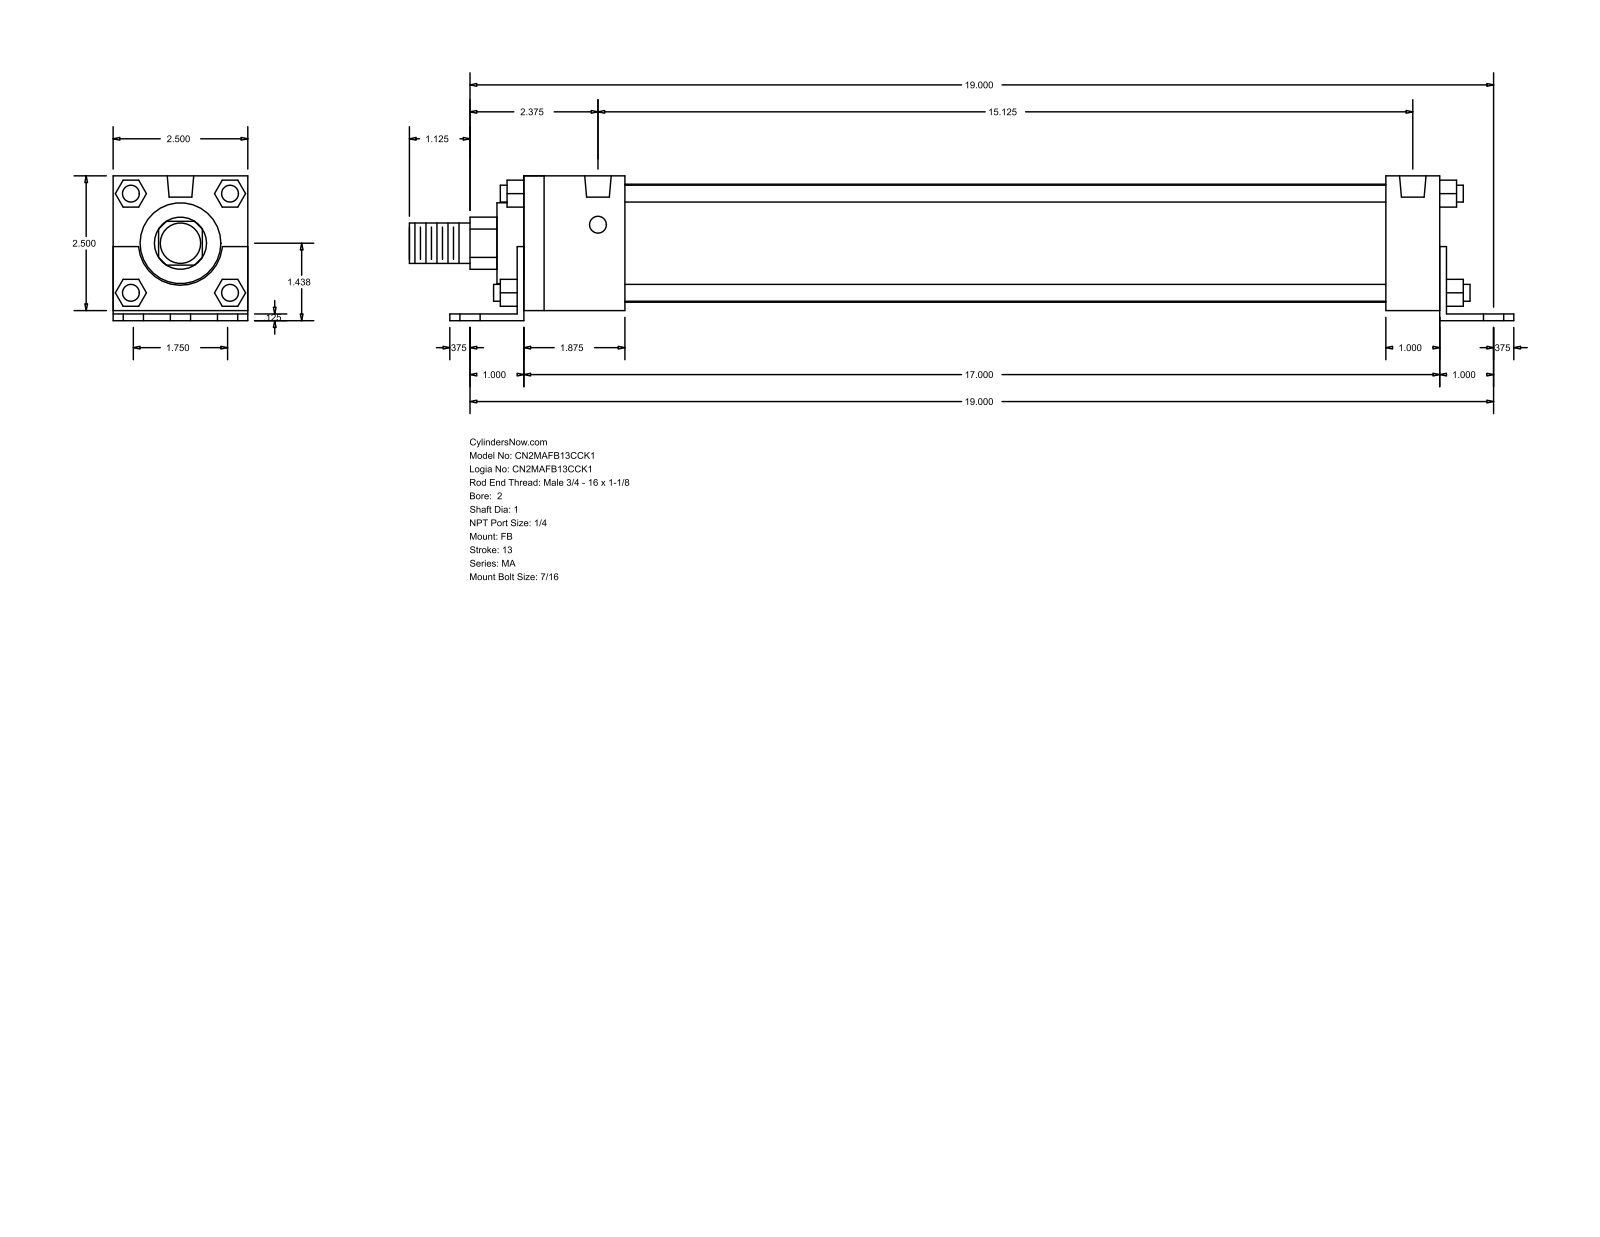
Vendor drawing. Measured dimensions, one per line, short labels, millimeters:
name: MA_FB__0200_1
written by: GSSL Pune (CONFIG_CONTROL_DESIGN)
unit: mm
bodies: 0 solids, 140 faces (105 planar, 35 cylindrical, 0 other)
size: 520.7 × 68.26 × 63.5
holes: 6× ⌀11.11, 4× ⌀7.94, 2× ⌀12.49
bosses: 4× ⌀7.94, 1× ⌀55.63, 1× ⌀38.1, 1× ⌀25.4, 1× ⌀19.05
rounds: 1× R12.29, 1× R19.81
face distances: 63.5, 3.17, 4.76, 68.26, 1.59, 65.09, 12.7, 3.18, 431.8, 434.98
hole spacings: 22.23, 483.11, 482.6, 44.11, 44.46, 64.3, 384.17, 422.85
